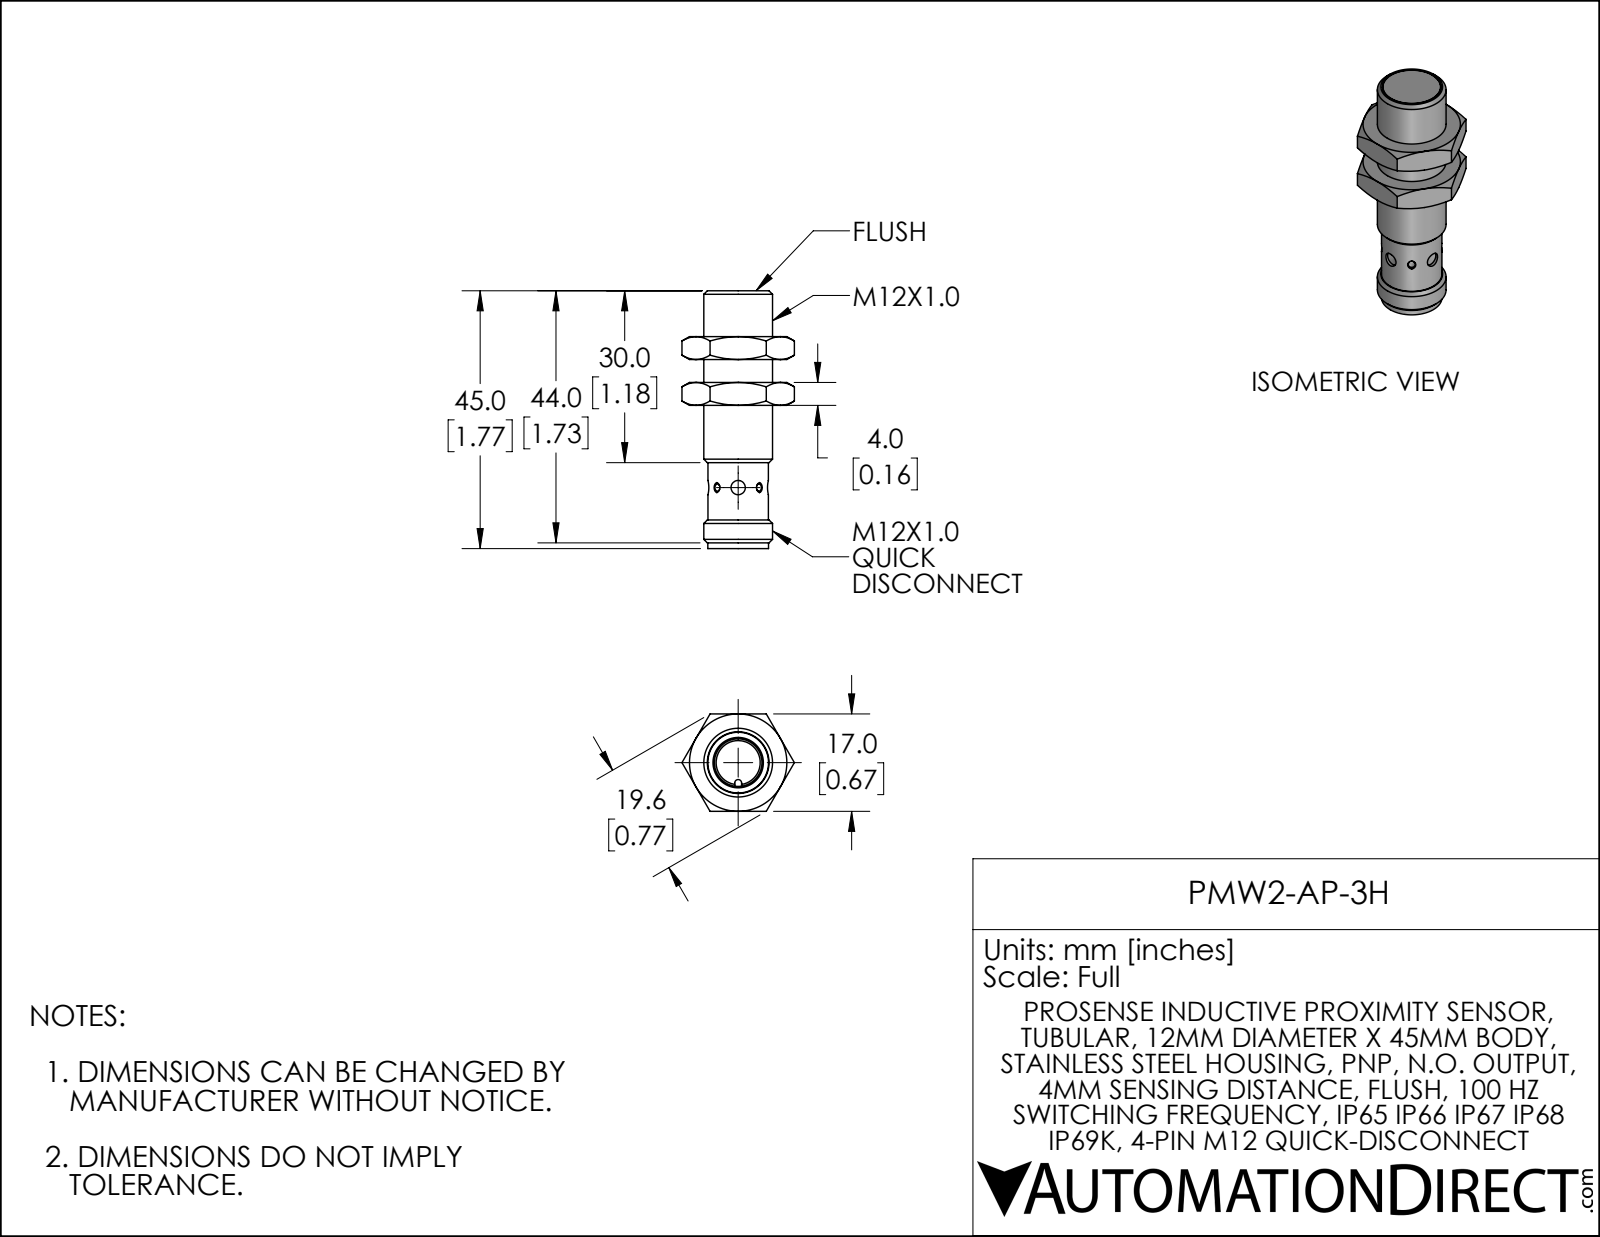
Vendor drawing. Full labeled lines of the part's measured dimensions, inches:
Part name (STEP PRODUCT): PMW2-AP-3H
STEP written by: SolidWorks 2019 (CONFIG_CONTROL_DESIGN)
Units: inches
Bodies: 3 solids, 88 faces (27 planar, 14 cylindrical, 47 other)
Overall size (bounding box): 1.772 × 0.773 × 0.669
Volume: 0.336 in³ · Surface area: 5.342 in²
Round holes (diameter × count): ⌀0.098 ×2, ⌀0.327 ×1, ⌀0.402 ×1, ⌀0.43 ×1
Round bosses / shafts (diameter × count): ⌀0.472 ×1, ⌀0.417 ×1, ⌀0.415 ×1, ⌀0.4 ×1
Partial cylindrical surfaces — rounded edges, fillets, slot ends (radius × count): R0.024 ×1
Main face-to-face distances: 0.157, 0.669, 0.315, 0.787, 0.63, 0.472, 0.634, 0.791, 0.949, 1.421
